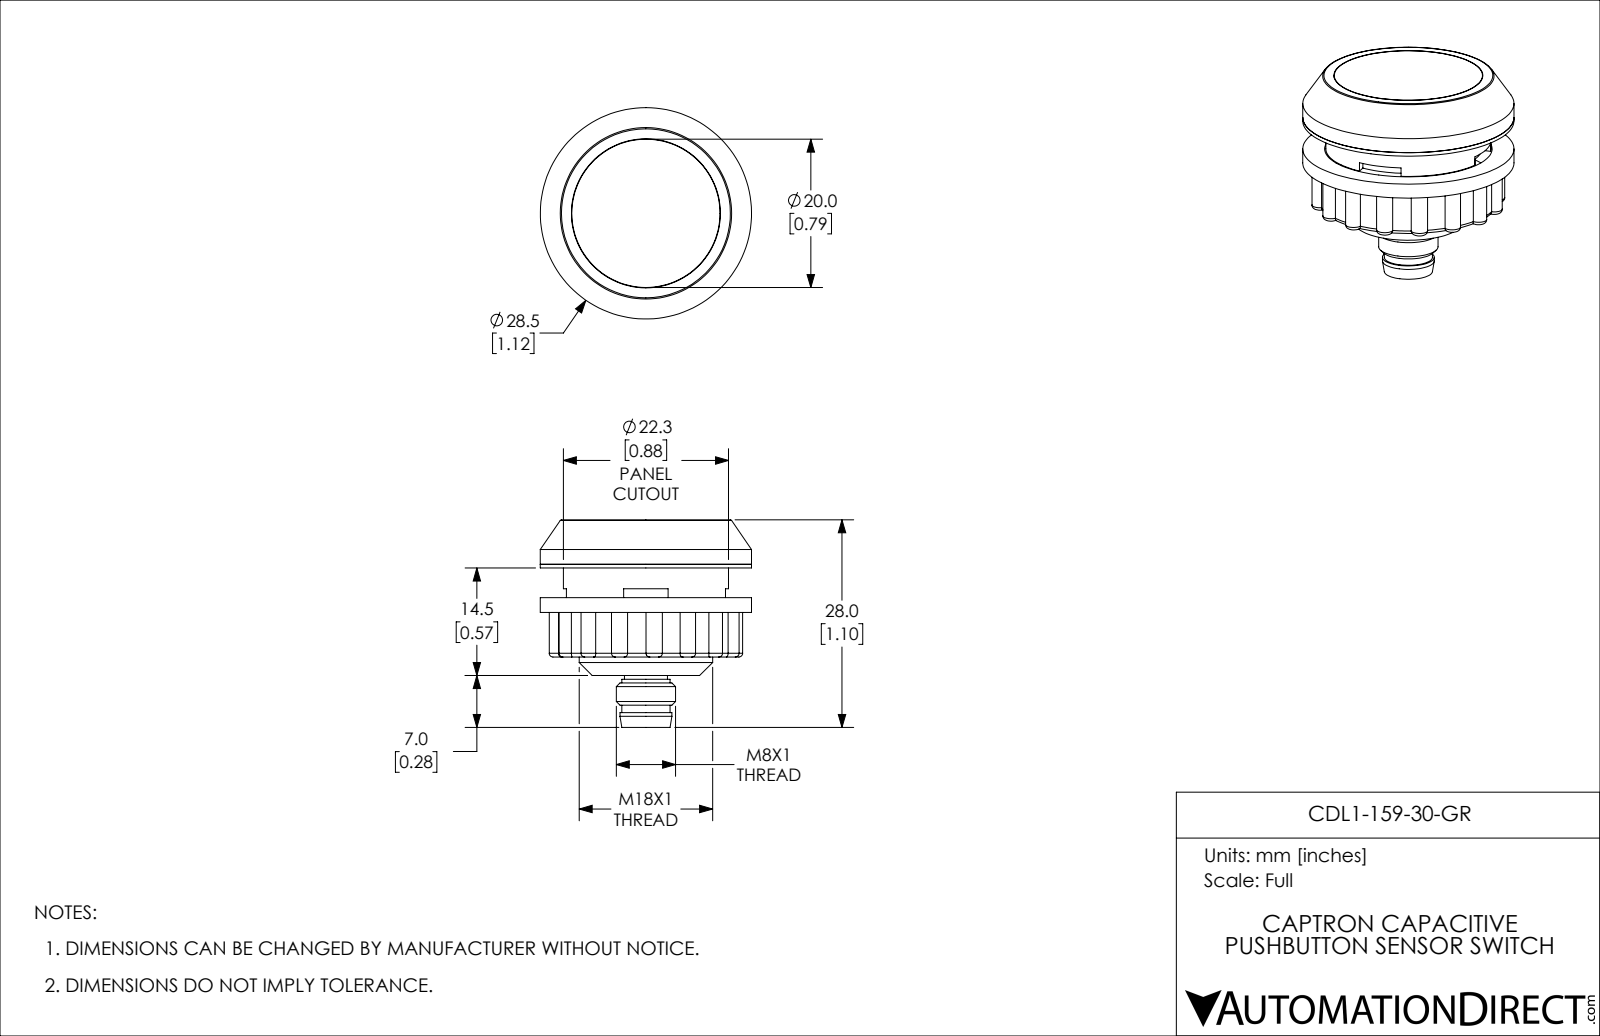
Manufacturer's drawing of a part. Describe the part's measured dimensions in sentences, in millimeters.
The part is named "CDL1-159-30-GR". Its 3-D file was written by "SolidWorks 2019 (CONFIG_CONTROL_DESIGN)". It is 10 solids with 213 faces: 39 planar, 99 cylindrical and 75 other. Overall it measures 28.5 by 28.5 by 28 millimeters. Its volume is 9 790 cubic millimeters and its surface area 7 226 square millimeters. Round holes: 2 of diameter 2, 1 of diameter 6, 1 of diameter 17, 1 of diameter 20.1, 1 of diameter 22.3, 1 of diameter 22.6. Round bosses or shafts: 4 of diameter 1, 1 of diameter 28.5, 1 of diameter 22.28, 1 of diameter 18, 1 of diameter 8, 1 of diameter 7, 1 of diameter 6.5, 1 of diameter 5.8. Partial cylindrical surfaces (rounded edges, fillets, slot ends): 16 of radius 1.1, 1 of radius 9.9, 1 of radius 12. The main face-to-face distances are 6, 3, 6.5, 10.5, 4, 4.5, 12.5, 7.5, 14.5, 8.2. The hole center spacings are 5.5, 11.
